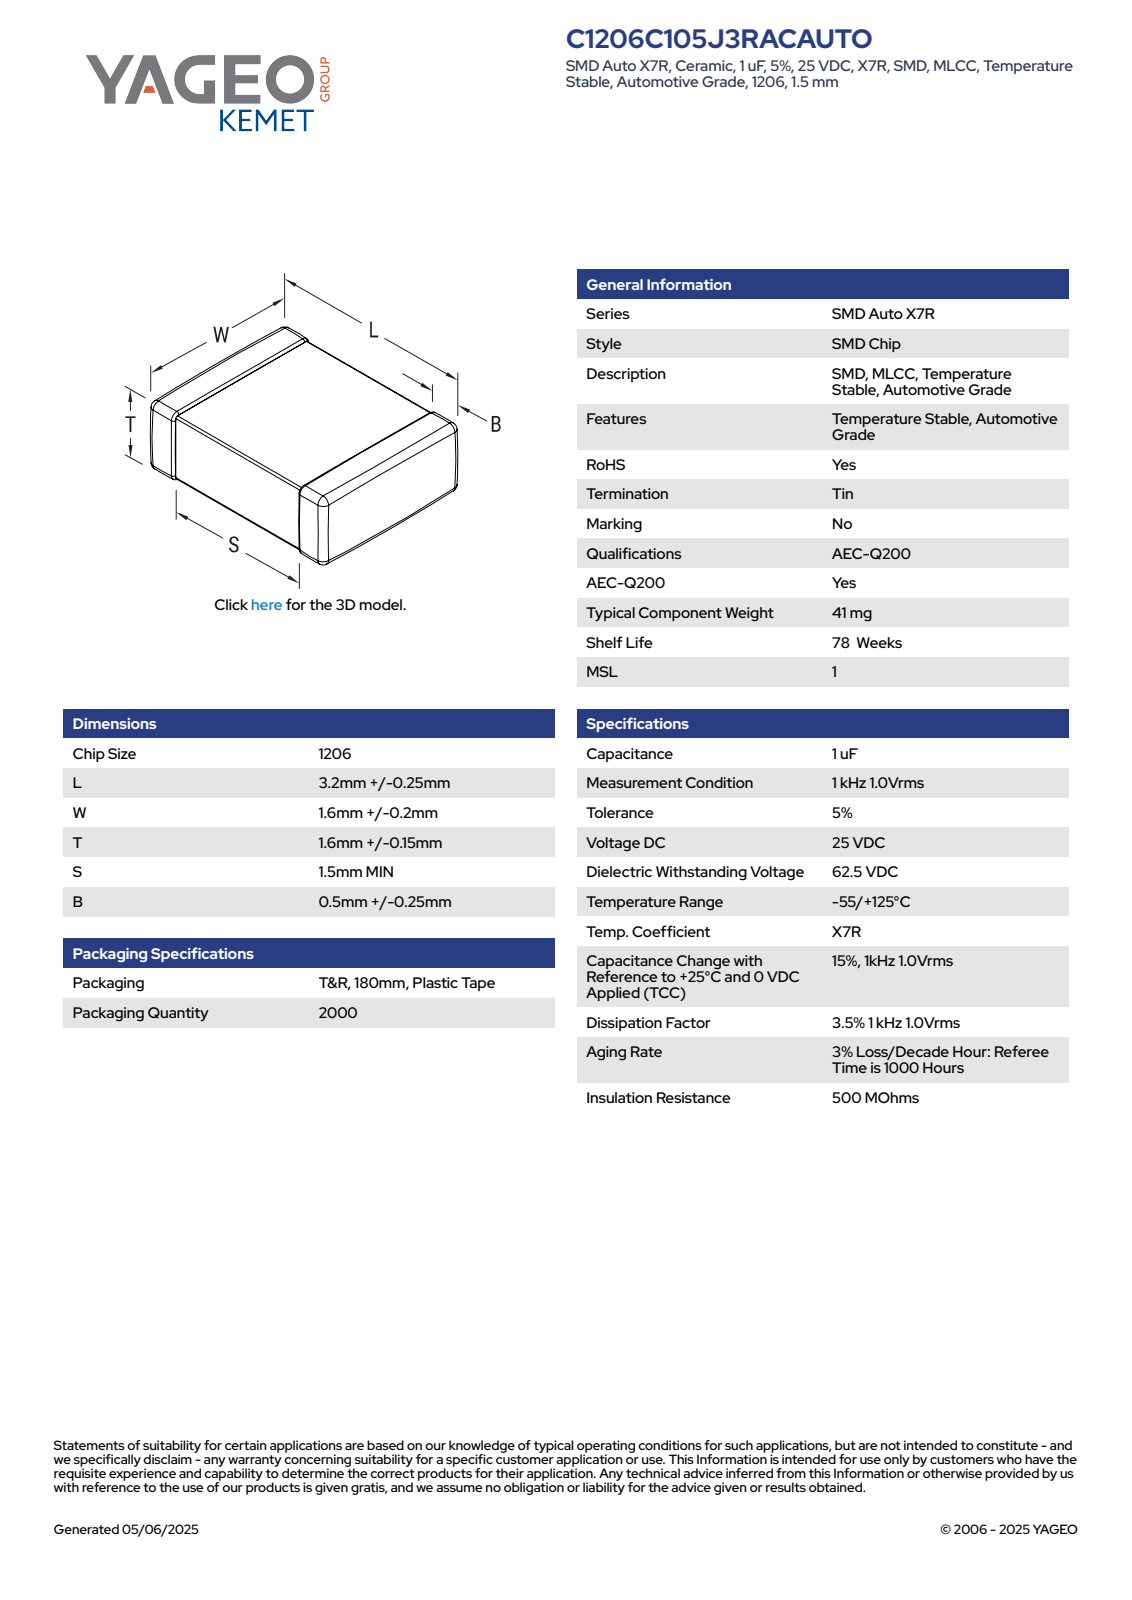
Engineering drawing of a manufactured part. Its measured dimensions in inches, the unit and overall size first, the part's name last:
Units: inches
Overall size (bounding box): 0.136 × 0.071 × 0.069
Main face-to-face distances: 0.067, 0.069, 0.068, 0.066, 0.136, 0.069, 0.071, 0.066, 0.03, 0.031
Volume: 0.001 in³ · Surface area: 0.047 in²
Bodies: 4 solids, 125 faces (71 planar, 38 cylindrical, 16 other)
Part name (STEP PRODUCT): CCS_CCSTDNOS_1206_L3.45W1.8T1.75B0.75
STEP written by: SolidWorks 2014 (AUTOMOTIVE_DESIGN)
